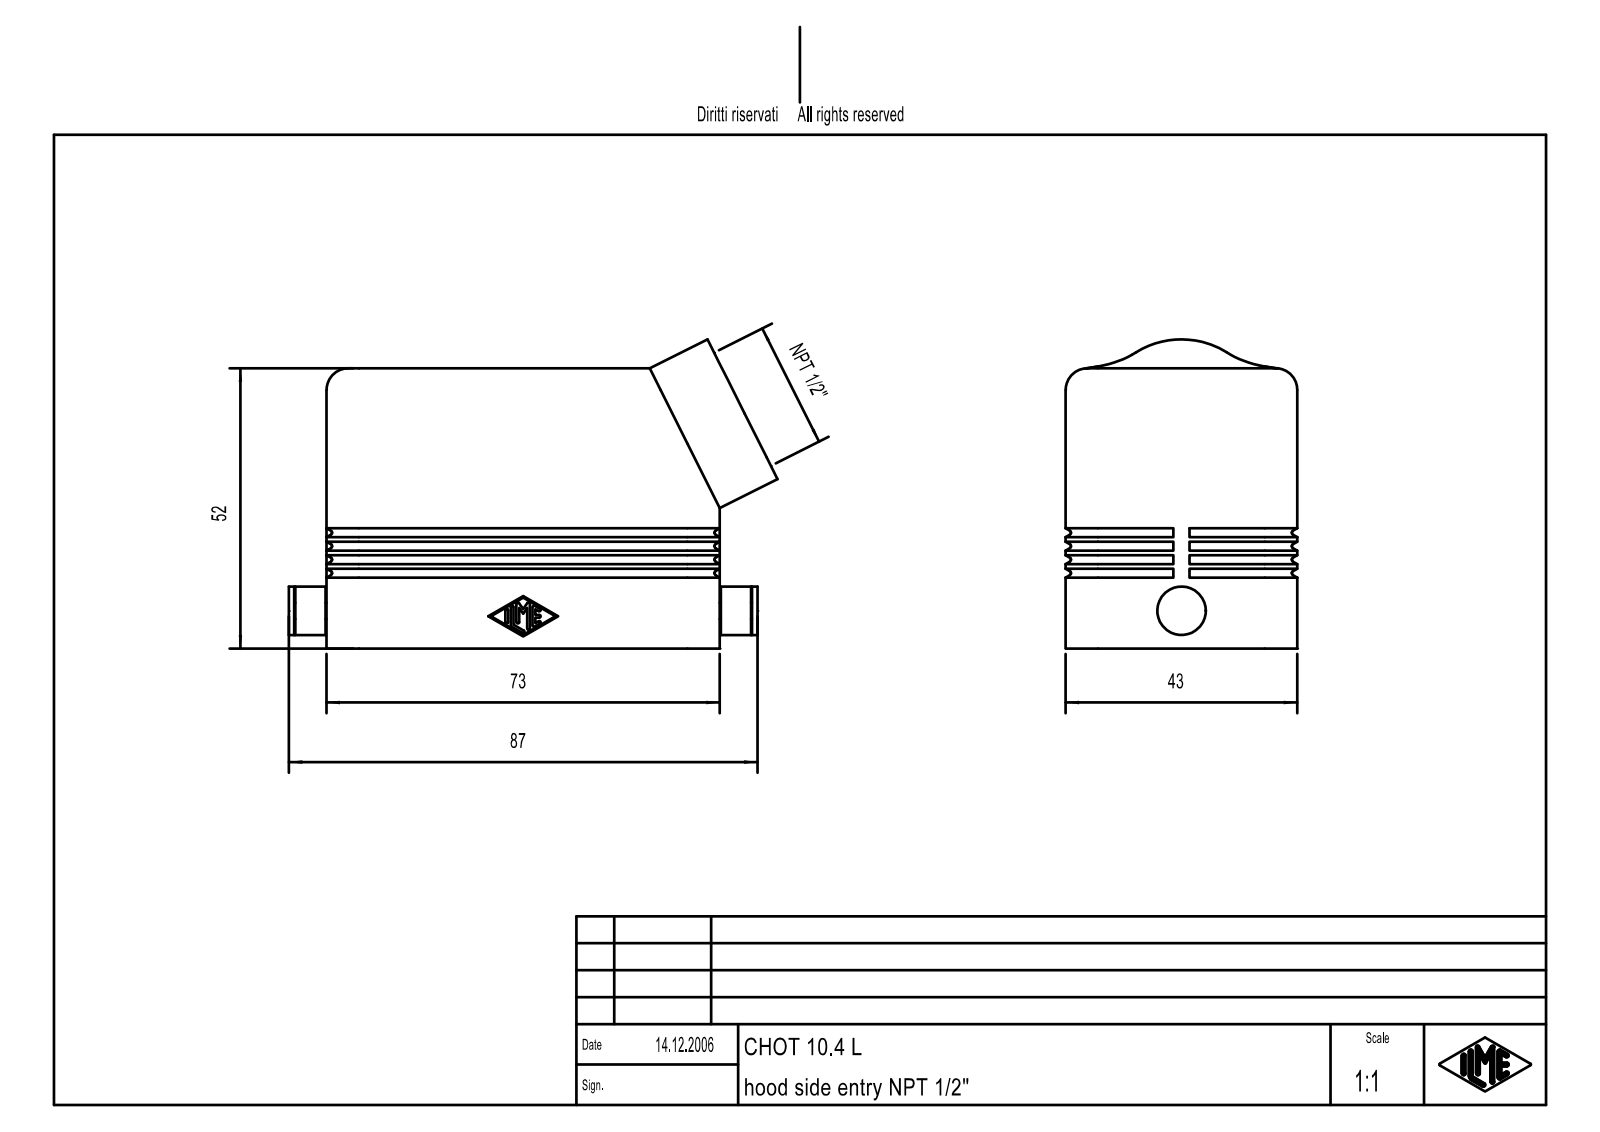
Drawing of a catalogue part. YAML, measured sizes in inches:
part_name: "MSBO7565"
step_written_by: "Creo Elements/Direct Modeling 18.0B 02-Dec-2011 (C) Parametric Technology GmbH (AUTOMOTIVE_DESIGN)"
units: inches
bodies: {solids: 1, faces: 403, planar: 178, cylindrical: 143, other: 82}
overall_size: [3.572, 2.259, 1.693]
volume: 3.255
surface_area: 46.17
round_holes:
  - {diameter: 0.097, count: 4}
  - {diameter: 0.122, count: 4}
  - {diameter: 0.72, count: 1}
round_bosses_or_shafts:
  - {diameter: 0.354, count: 1}
  - {diameter: 0.118, count: 1}
partial_cylinders:
  - {radius: 0.016, count: 32}
  - {radius: 0.01, count: 14}
  - {radius: 0.059, count: 4}
  - {radius: 0.118, count: 4}
  - {radius: 0.197, count: 4}
  - {radius: 0.236, count: 4}
  - {radius: 0.157, count: 3}
face_to_face_distances: [0.118, 1.575, 1.693, 1.457, 0.453, 0.335, 2.756, 2.421, 2.303, 1.24]
hole_center_spacings: [1.063, 2.244, 2.483]
